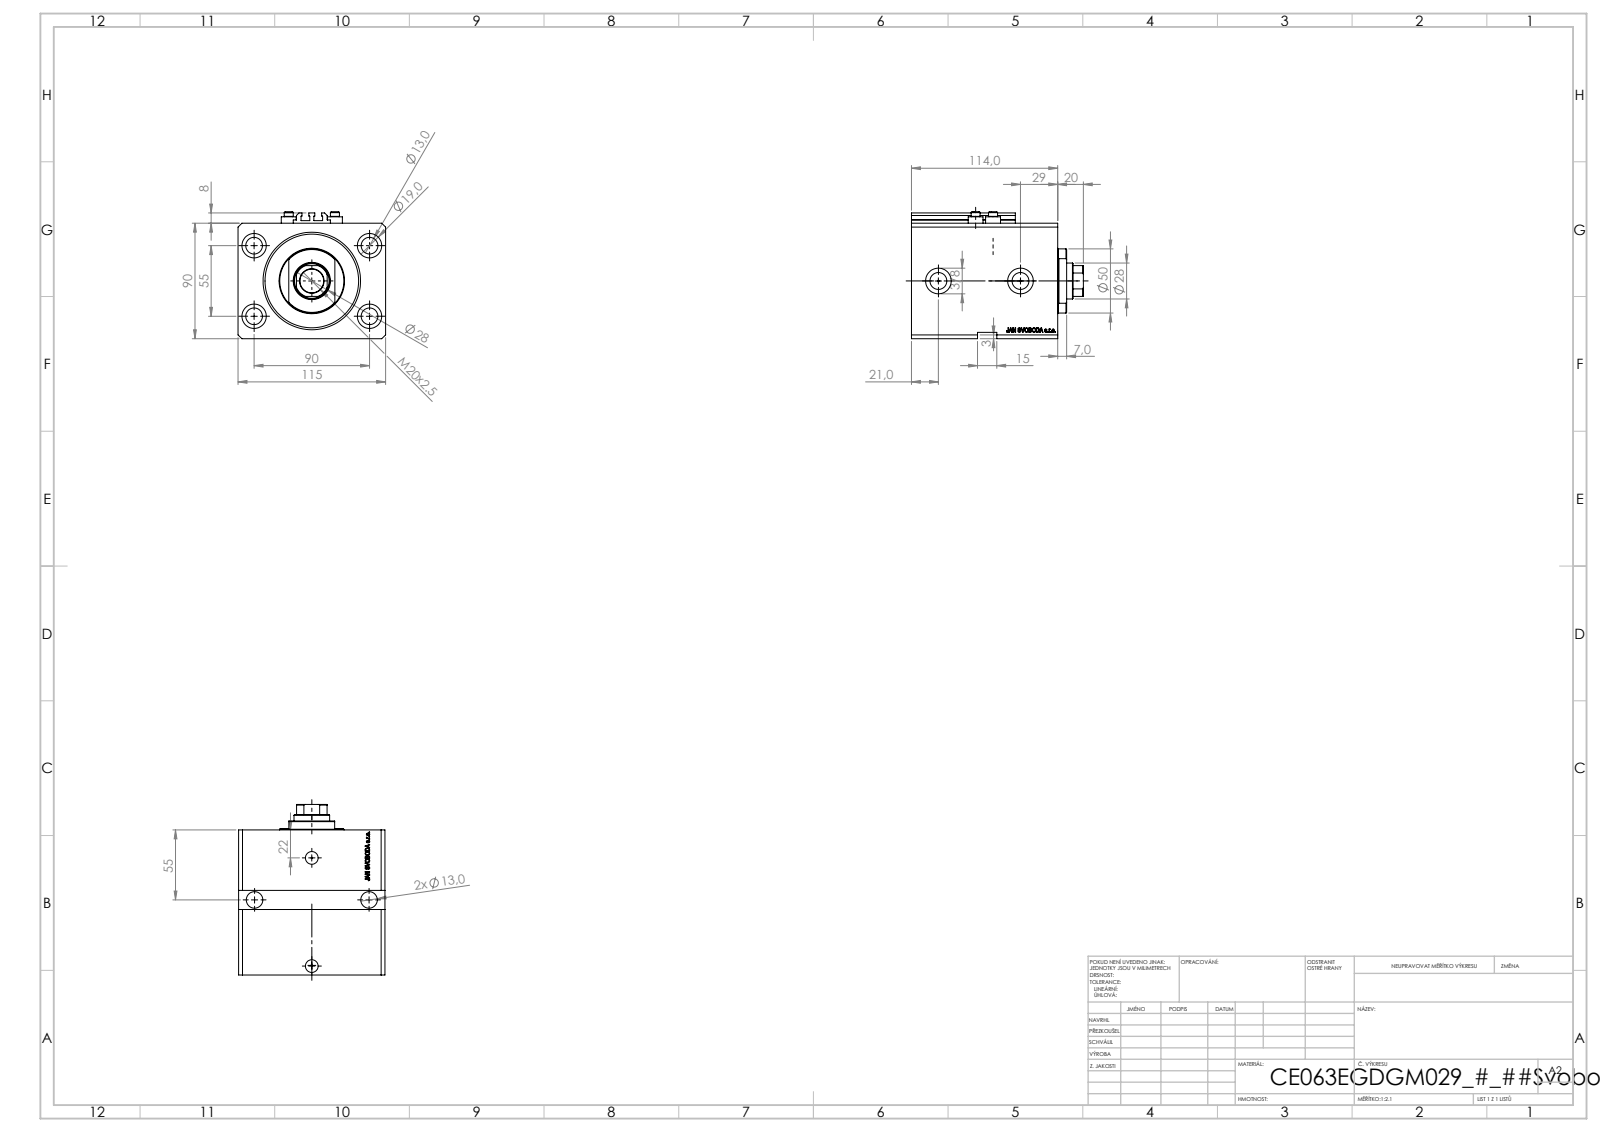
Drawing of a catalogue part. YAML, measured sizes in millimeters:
part_name: "V250CE_VC_E; V250CE_C_VCP; ALLEN BOLT V250CE; V250CE_E_Body"
step_written_by: "SolidWorks 2019 (CONFIG_CONTROL_DESIGN)"
units: millimeters
bodies: {solids: 8, faces: 1123, planar: 547, cylindrical: 138, other: 438}
overall_size: [134, 115, 99]
volume: 1018000
surface_area: 163710
round_holes:
  - {diameter: 13, count: 6}
  - {diameter: 1.25, count: 4}
  - {diameter: 4, count: 4}
  - {diameter: 19, count: 4}
  - {diameter: 10, count: 2}
  - {diameter: 13.16, count: 2}
  - {diameter: 20, count: 2}
  - {diameter: 18.5, count: 1}
  - {diameter: 28, count: 1}
  - {diameter: 63, count: 1}
  - {diameter: 76, count: 1}
round_bosses_or_shafts:
  - {diameter: 11.6, count: 4}
  - {diameter: 7, count: 4}
  - {diameter: 50, count: 1}
partial_cylinders:
  - {radius: 0.2, count: 10}
  - {radius: 13.5, count: 1}
face_to_face_distances: [90, 115, 114, 96.1, 20, 17.9, 94, 76.1, 49, 29]
hole_center_spacings: [52.74, 90, 13.6, 27.39, 28.46, 33.62, 36, 38.48]
